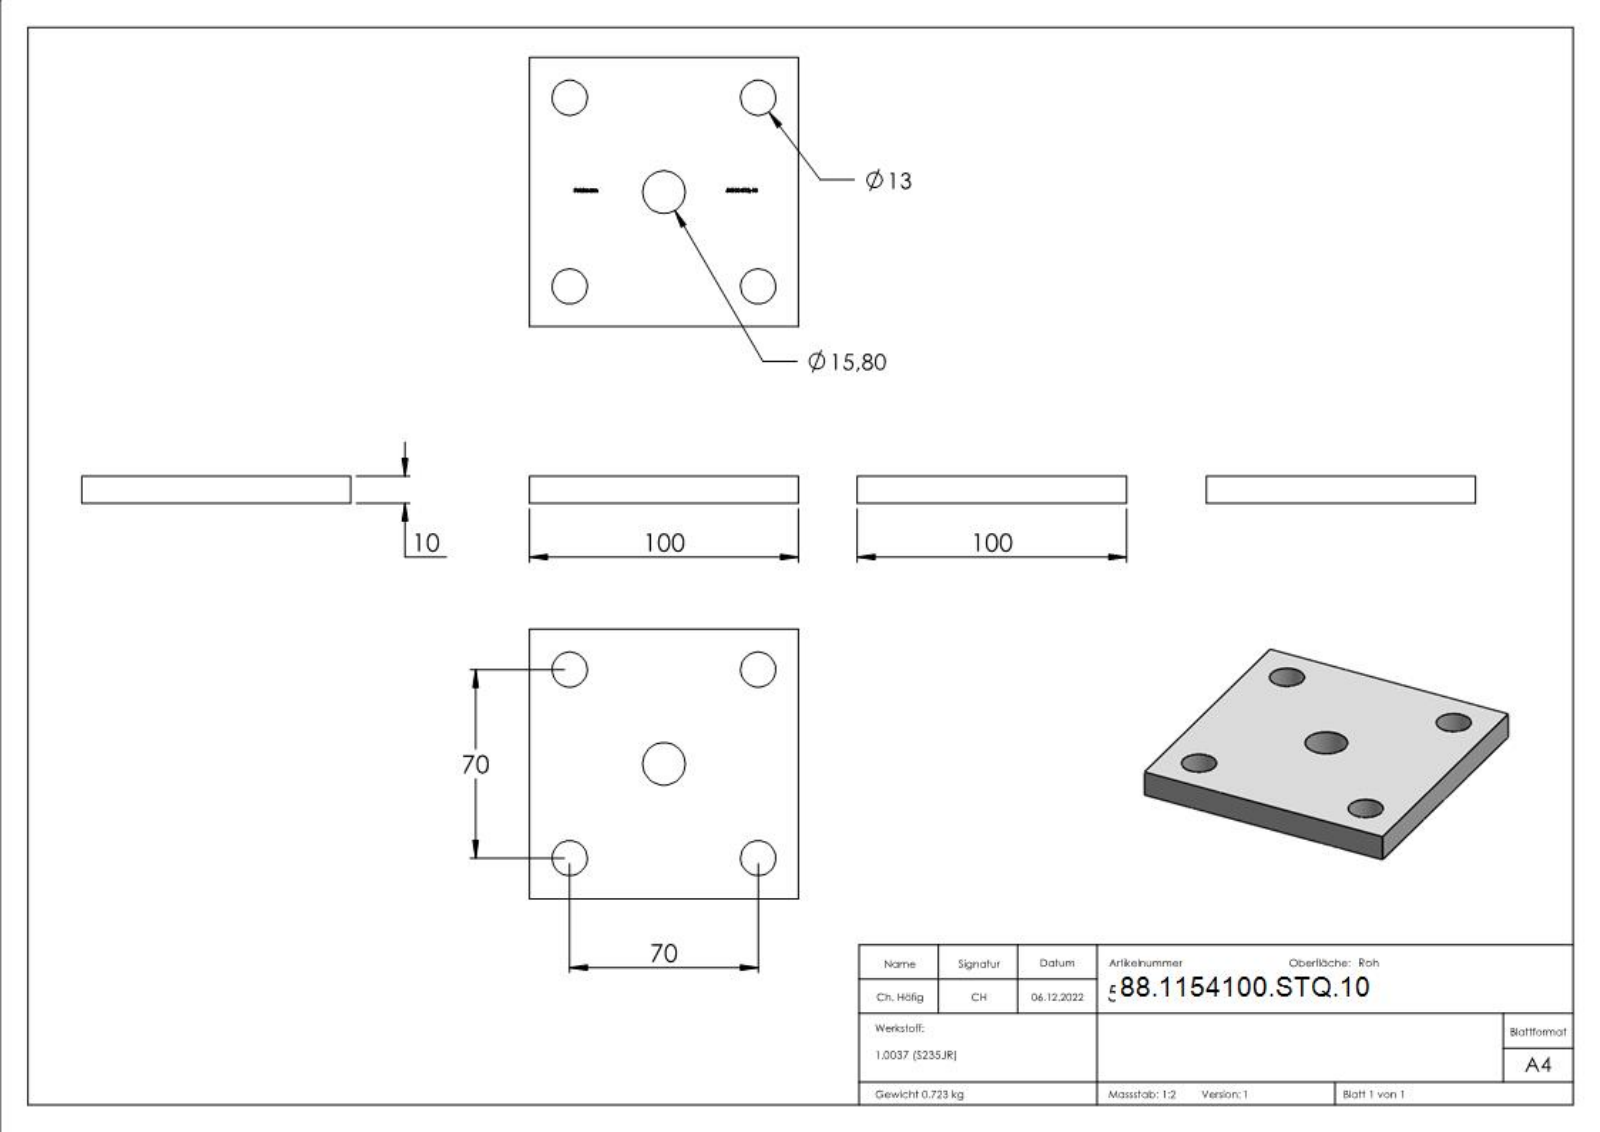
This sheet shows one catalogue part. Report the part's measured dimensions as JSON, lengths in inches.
{"part_name": "54100-STQ-10", "step_written_by": "SolidWorks 2018 (CONFIG_CONTROL_DESIGN)", "units": "inches", "bodies": {"solids": 1, "faces": 256, "planar": 143, "cylindrical": 5, "other": 108}, "overall_size": [3.937, 3.937, 0.394], "volume_in3": 5.659, "surface_area_in2": 38.26, "round_holes": [[0.512, 4], [0.622, 1]], "face_to_face_distances": [0.394, 3.937, 0.39, 1.969, 1.986, 0.296, 0.035, 0.174, 0.122, 2.02], "hole_center_spacings": [1.949, 2.756, 3.897]}
